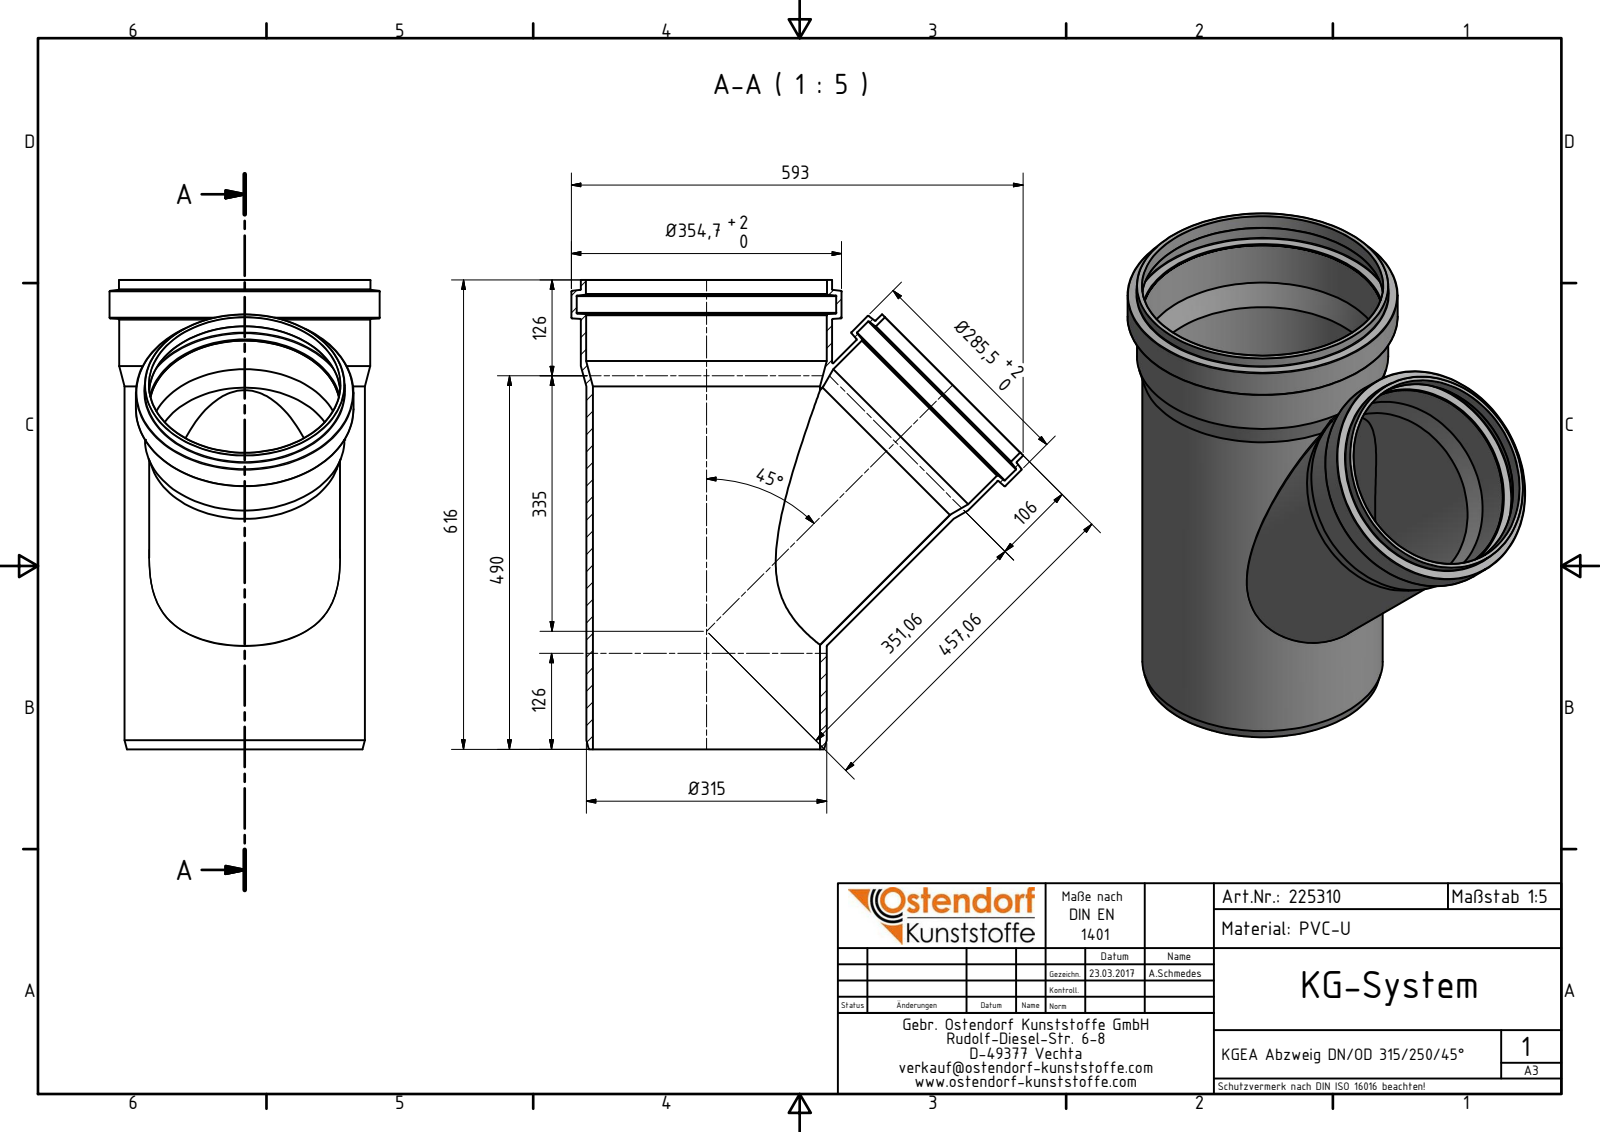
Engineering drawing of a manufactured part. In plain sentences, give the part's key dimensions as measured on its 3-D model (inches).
The part is named "225310 KGEA Abzweig DN_OD 315_250_45°". Its 3-D file was written by "Autodesk Inventor 2016 (AUTOMOTIVE_DESIGN)". It is 1 solid with 64 faces: 5 planar, 18 cylindrical and 41 other. Overall it measures 24.252 by 23.346 by 13.965 inches. Its volume is 370.6 cubic inches and its surface area 2 472 square inches. Round holes: 2 of diameter 9.886, 1 of diameter 9.303, 1 of diameter 9.874, 1 of diameter 10.807, 1 of diameter 11.74, 1 of diameter 12.441, 1 of diameter 12.453, 1 of diameter 13.421. Round bosses or shafts: 1 of diameter 13.965, 1 of diameter 12.996, 1 of diameter 12.984, 1 of diameter 12.425, 1 of diameter 11.24, 1 of diameter 10.319, 1 of diameter 10.307, 1 of diameter 9.862. The main face-to-face distances are 24.252, 22.419, 1.833, 1.702.
